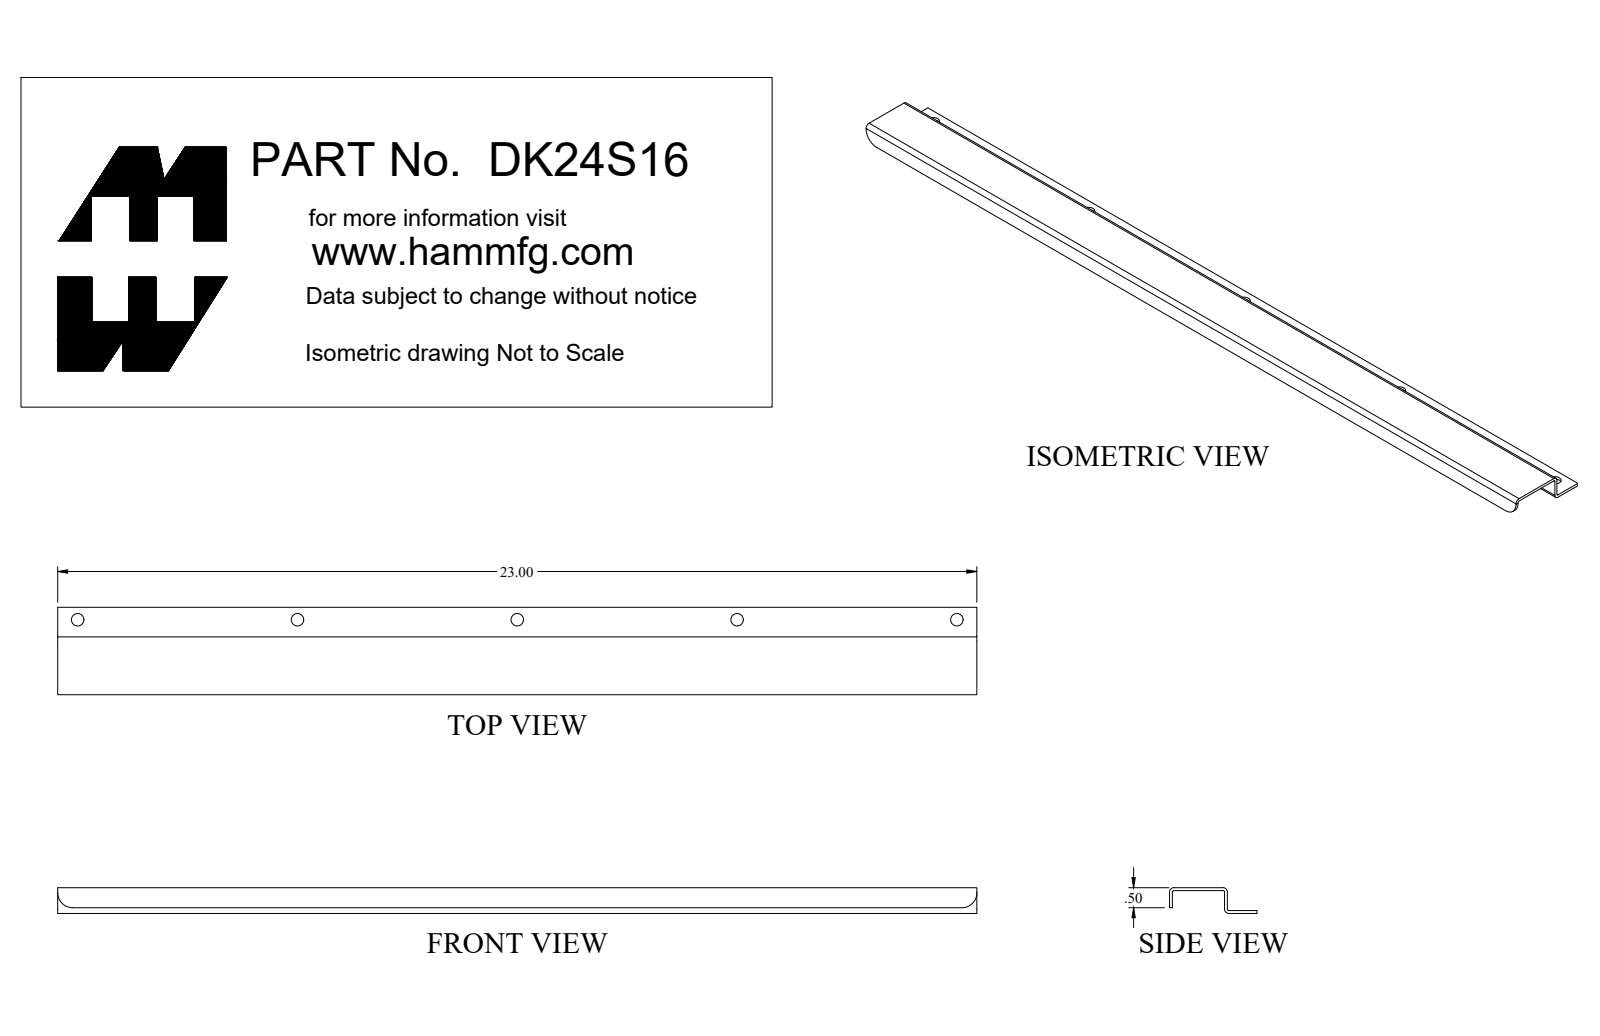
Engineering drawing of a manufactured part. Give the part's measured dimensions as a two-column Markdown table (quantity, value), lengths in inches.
| quantity | value |
| --- | --- |
| part name | DK24S16_Default |
| STEP written by | SolidWorks 2018 (CONFIG_CONTROL_DESIGN) |
| units | inches |
| bodies | 5 solids, 69 faces (35 planar, 28 cylindrical, 6 other) |
| overall size | 23 × 2.188 × 1.322 |
| volume | 6.292 in³ |
| surface area | 185.7 in² |
| round holes (diameter × count) | 0.313 × 5, 0.201 × 1, 0.275 × 1 |
| round bosses / shafts (diameter × count) | 0.625 × 1, 0.483 × 1, 0.25 × 1 |
| partial cylindrical surfaces (radius × count) | 0.036 × 3, 0.108 × 3, 0.375 × 2 |
| main face-to-face distances | 0.072, 0.572, 0.644, 1.376, 0.5, 0.063, 0.635, 0.707, 0.135, 1.448 |
| hole center spacings | 5.5, 11, 16.5, 22 |
